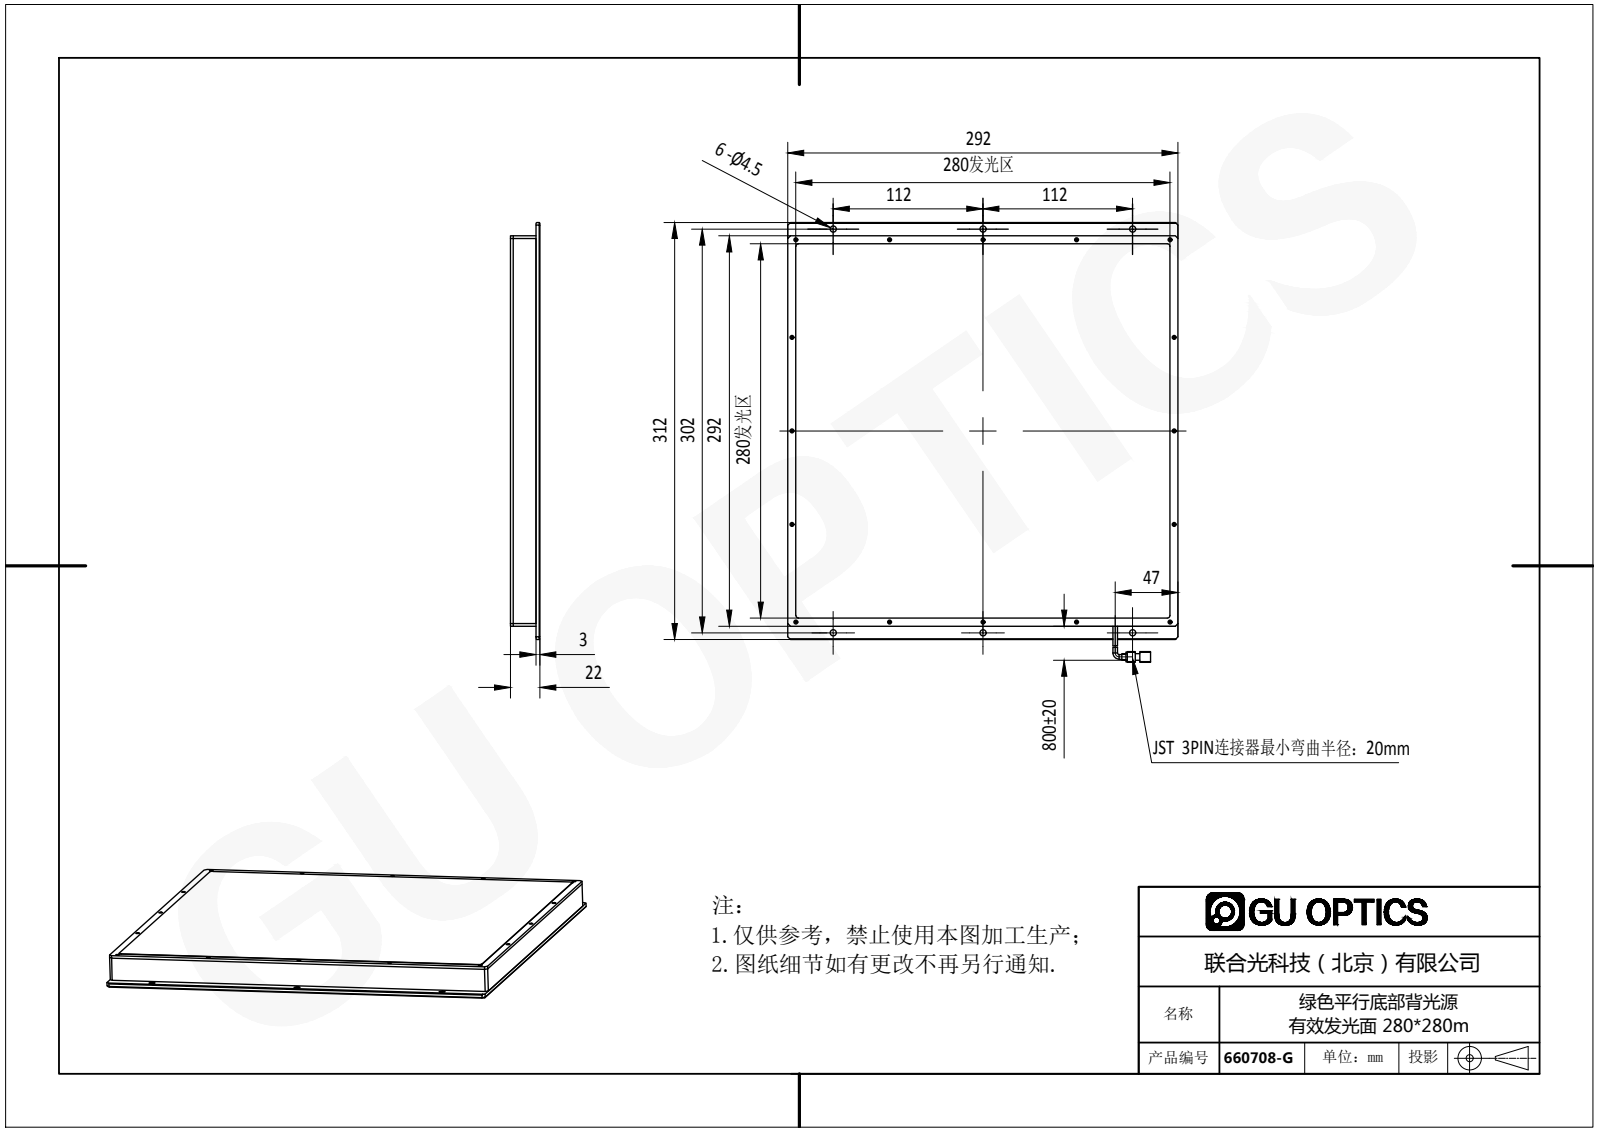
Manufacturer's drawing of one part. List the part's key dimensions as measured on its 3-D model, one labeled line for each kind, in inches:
Part name (STEP PRODUCT): 660708-G
STEP written by: SolidWorks 2016 (AUTOMOTIVE_DESIGN)
Units: inches
Bodies: 5 solids, 652 faces (220 planar, 274 cylindrical, 158 other)
Overall size (bounding box): 12.953 × 11.496 × 0.87
Volume: 34.46 in³ · Surface area: 640.7 in²
Round holes (diameter × count): ⌀0.063 ×32, ⌀0.049 ×16, ⌀0.059 ×16, ⌀0.079 ×16, ⌀0.094 ×16, ⌀0.11 ×16, ⌀0.177 ×6
Round bosses / shafts (diameter × count): ⌀0.138 ×2
Partial cylindrical surfaces — rounded edges, fillets, slot ends (radius × count): R0.02 ×8, R0.039 ×8, R0.079 ×6
Main face-to-face distances: 0.669, 0.118, 0.787, 0.752, 0.87, 0.083, 0.236, 11.26, 11.496, 11.024
Hole centre spacings: 11.692, 3.15, 11.26, 4.155, 6.299, 7.261, 8.268, 10.394
